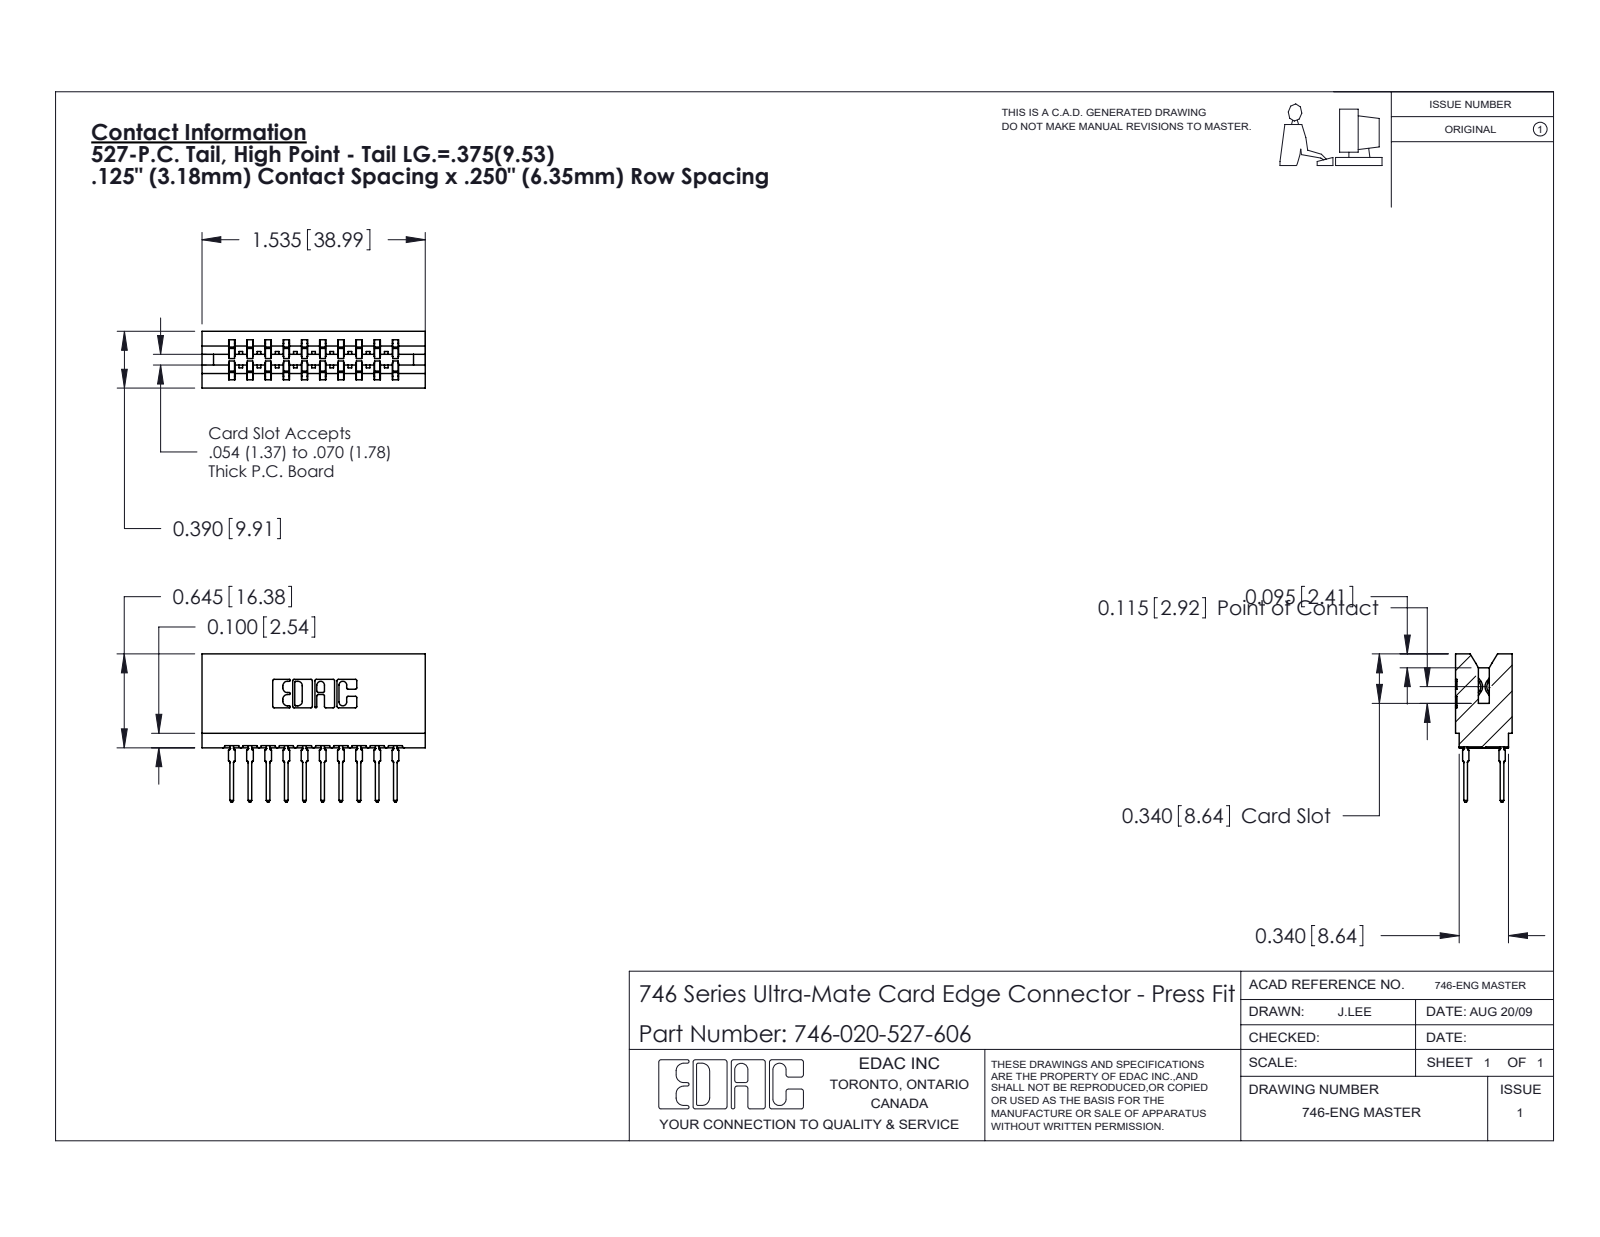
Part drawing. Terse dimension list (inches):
name: 746-020-527-606; 746 Part_.340 Slot Depth - 06; 746-292-001_527
written by: SolidWorks 2020 (CONFIG_CONTROL_DESIGN)
unit: in
bodies: 21 solids, 1888 faces (976 planar, 392 cylindrical, 520 other)
size: 1.535 × 1.019 × 0.39
volume: 0.285 in³; area: 9.987 in²
rounds: 40× R0.021, 22× R0.01, 11× R0.015, 8× R0.005, 8× R0.011, 6× R0.007, 6× R0.031, 3× R0.026
face distances: 0.25, 0.057, 0.333, 0.5, 0.042, 0.125, 0.75, 0.125, 0.39, 0.292
